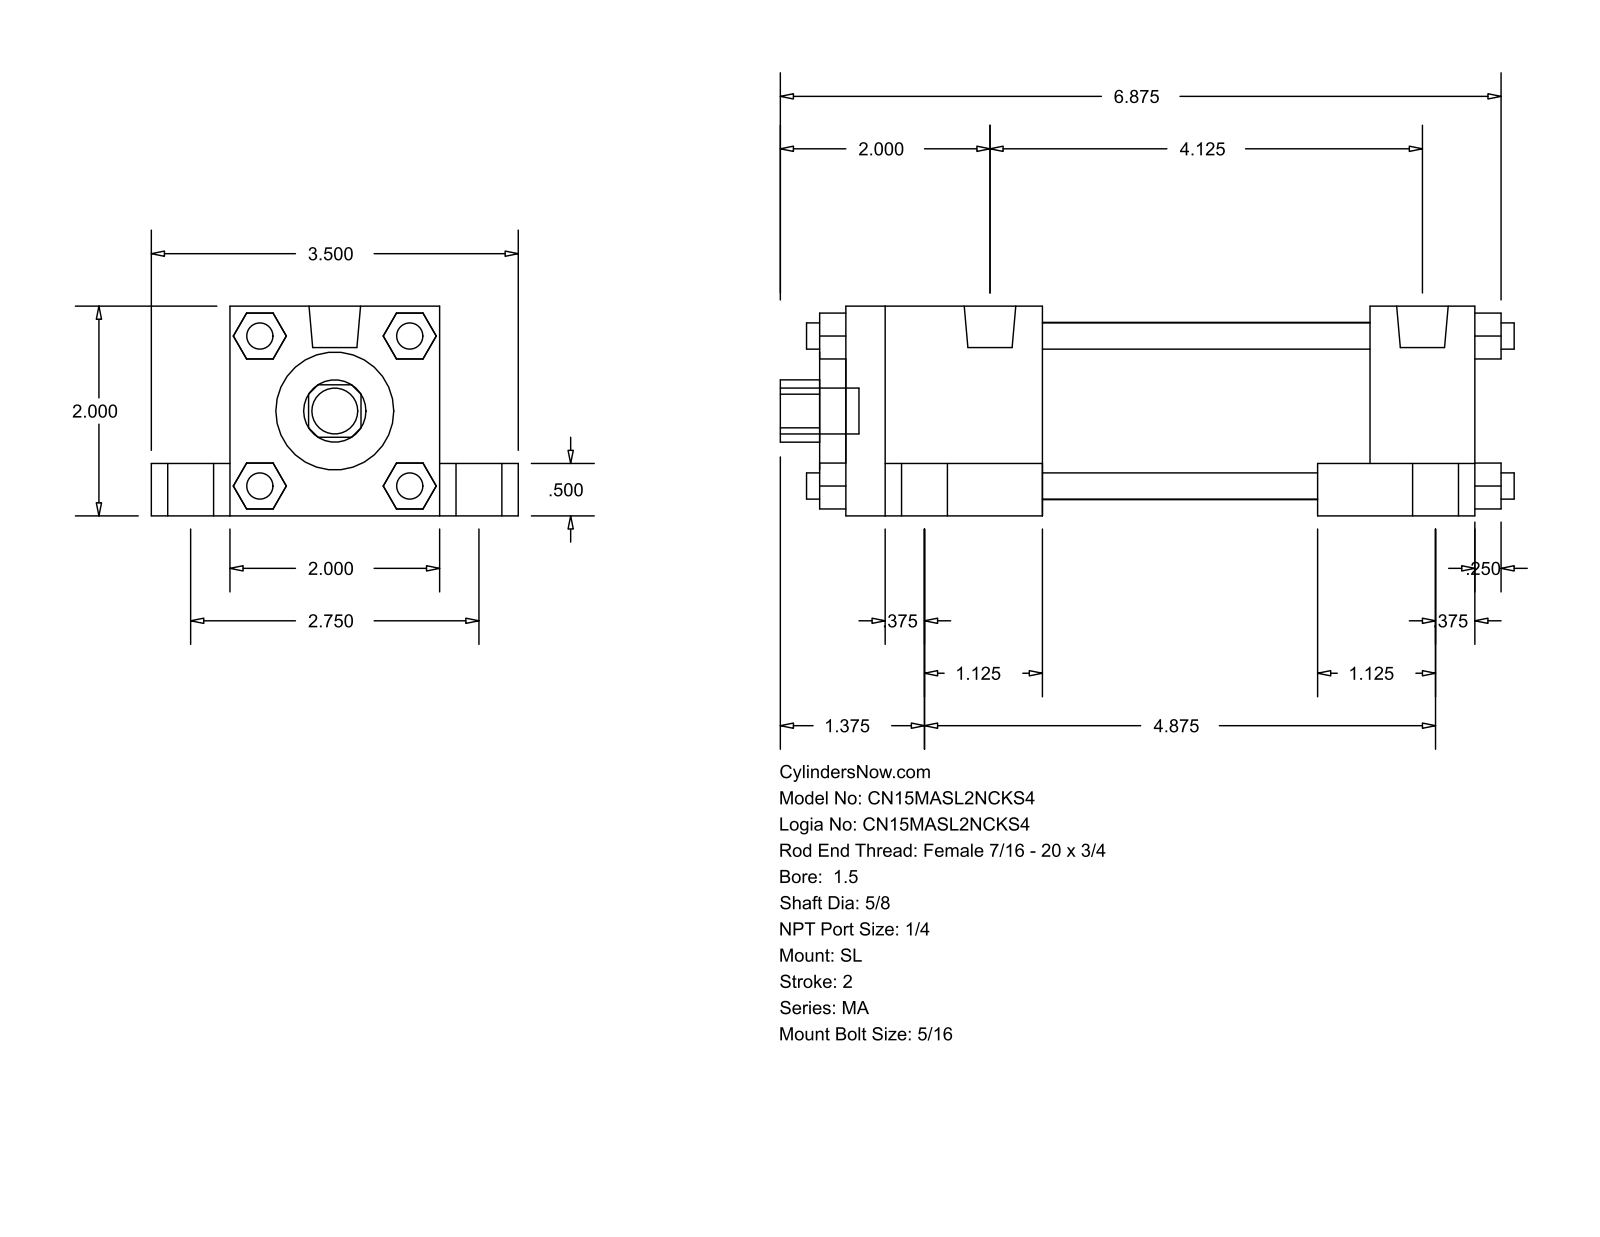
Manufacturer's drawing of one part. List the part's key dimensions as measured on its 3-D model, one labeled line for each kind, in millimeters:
Part name (STEP PRODUCT): MA_SL__0150_0.625
STEP written by: GSSL Pune (CONFIG_CONTROL_DESIGN)
Units: millimetres
Bodies: 0 solids, 148 faces (112 planar, 36 cylindrical, 0 other)
Overall size (bounding box): 177.8 × 88.9 × 50.8
Round holes (diameter × count): ⌀15.88 ×1, ⌀28.57 ×1, ⌀42.93 ×1
Round bosses / shafts (diameter × count): ⌀11.11 ×5, ⌀17.46 ×4, ⌀7.94 ×4, ⌀6.35 ×4, ⌀12.49 ×2
Partial cylindrical surfaces — rounded edges, fillets, slot ends (radius × count): R7.54 ×1
Main face-to-face distances: 50.8, 19.05, 38.1, 12.7, 152.4, 69.85, 9.52, 25.4, 127, 47.62
